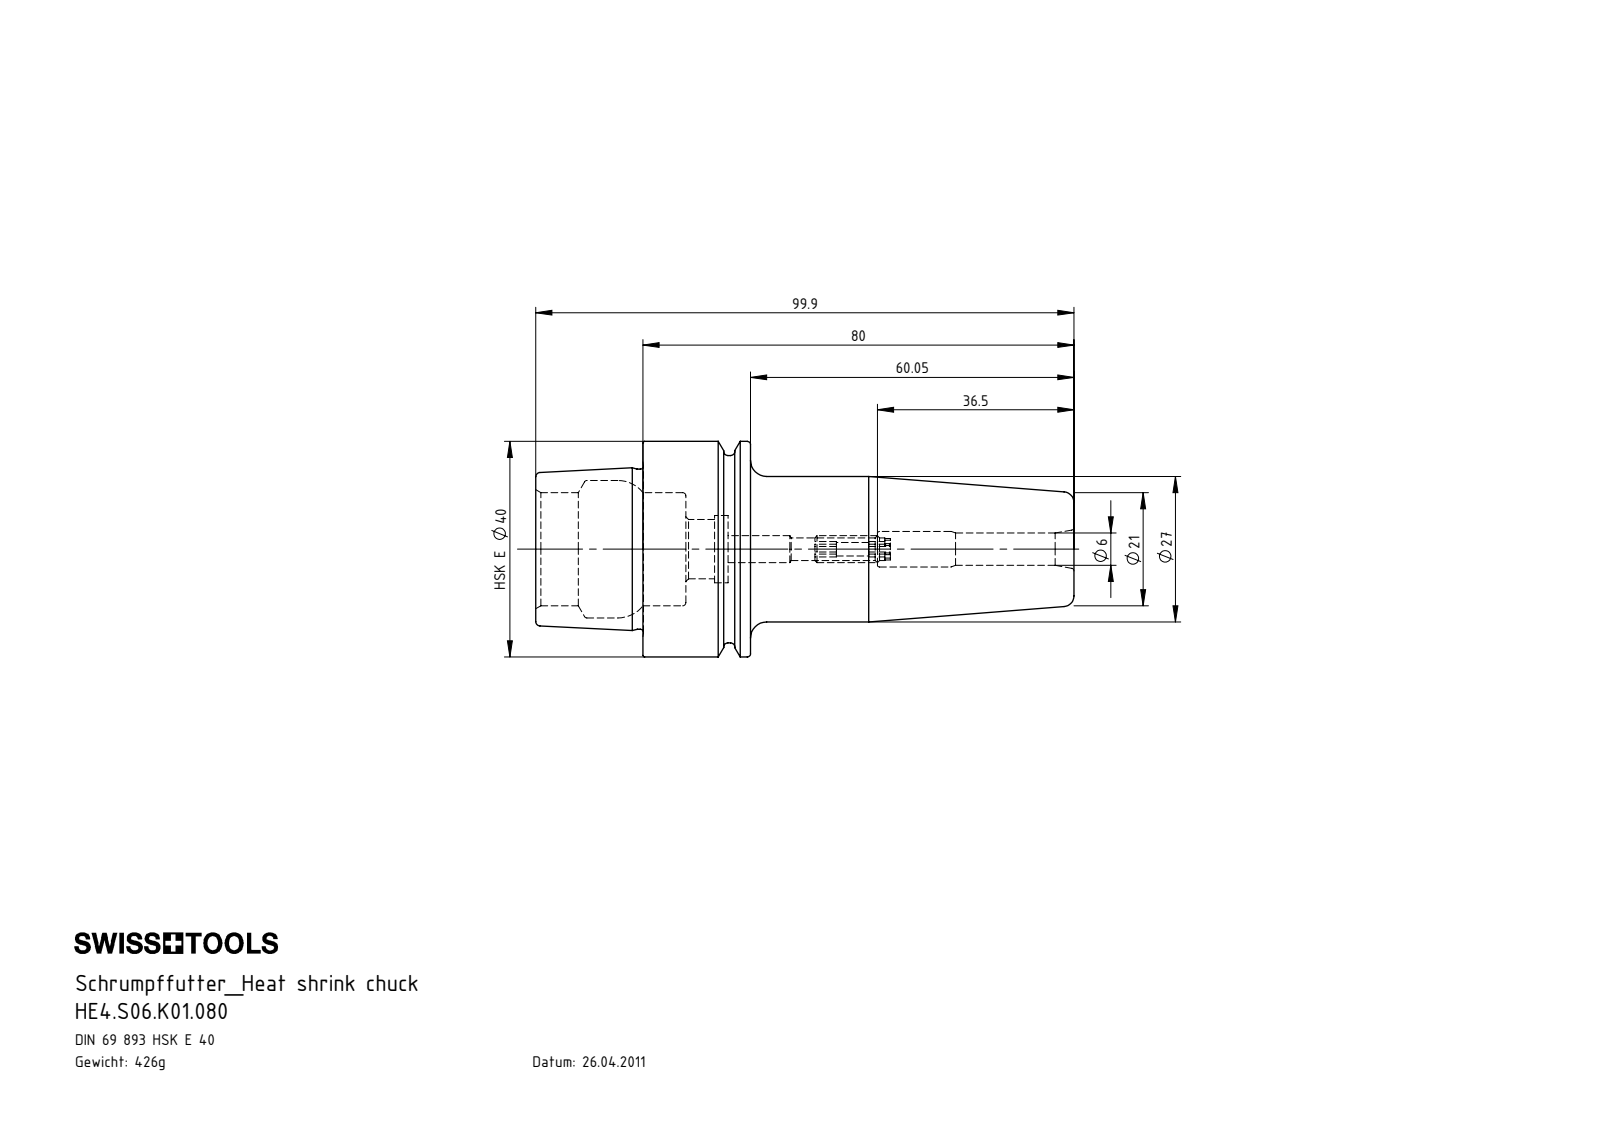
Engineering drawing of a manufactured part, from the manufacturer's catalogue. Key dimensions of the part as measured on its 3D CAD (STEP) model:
Part name (STEP PRODUCT): HE4-S06.K01.080; ERU-AN1.K01.014_A; HE4-S06.K01.080_B_Fertigbearbeitung
STEP written by: SolidWorks 2012 (AUTOMOTIVE_DESIGN)
Units: millimetres
Bodies: 2 solids, 137 faces (43 planar, 34 cylindrical, 60 other)
Overall size (bounding box): 99.9 × 40 × 40
Volume: 54 221 mm³ · Surface area: 15 220 mm²
Round holes (diameter × count): ⌀2.5 ×1, ⌀4.2 ×1, ⌀5 ×1, ⌀6 ×1, ⌀6.6 ×1, ⌀11 ×1, ⌀12.5 ×1, ⌀21 ×1, ⌀25.5 ×1
Round bosses / shafts (diameter × count): ⌀40 ×1, ⌀34.75 ×1, ⌀29.71 ×1, ⌀27 ×1
Main face-to-face distances: 19.95, 7.95, 12, 19.9, 27.85, 39.85, 99.9, 80, 72.05, 60.05
